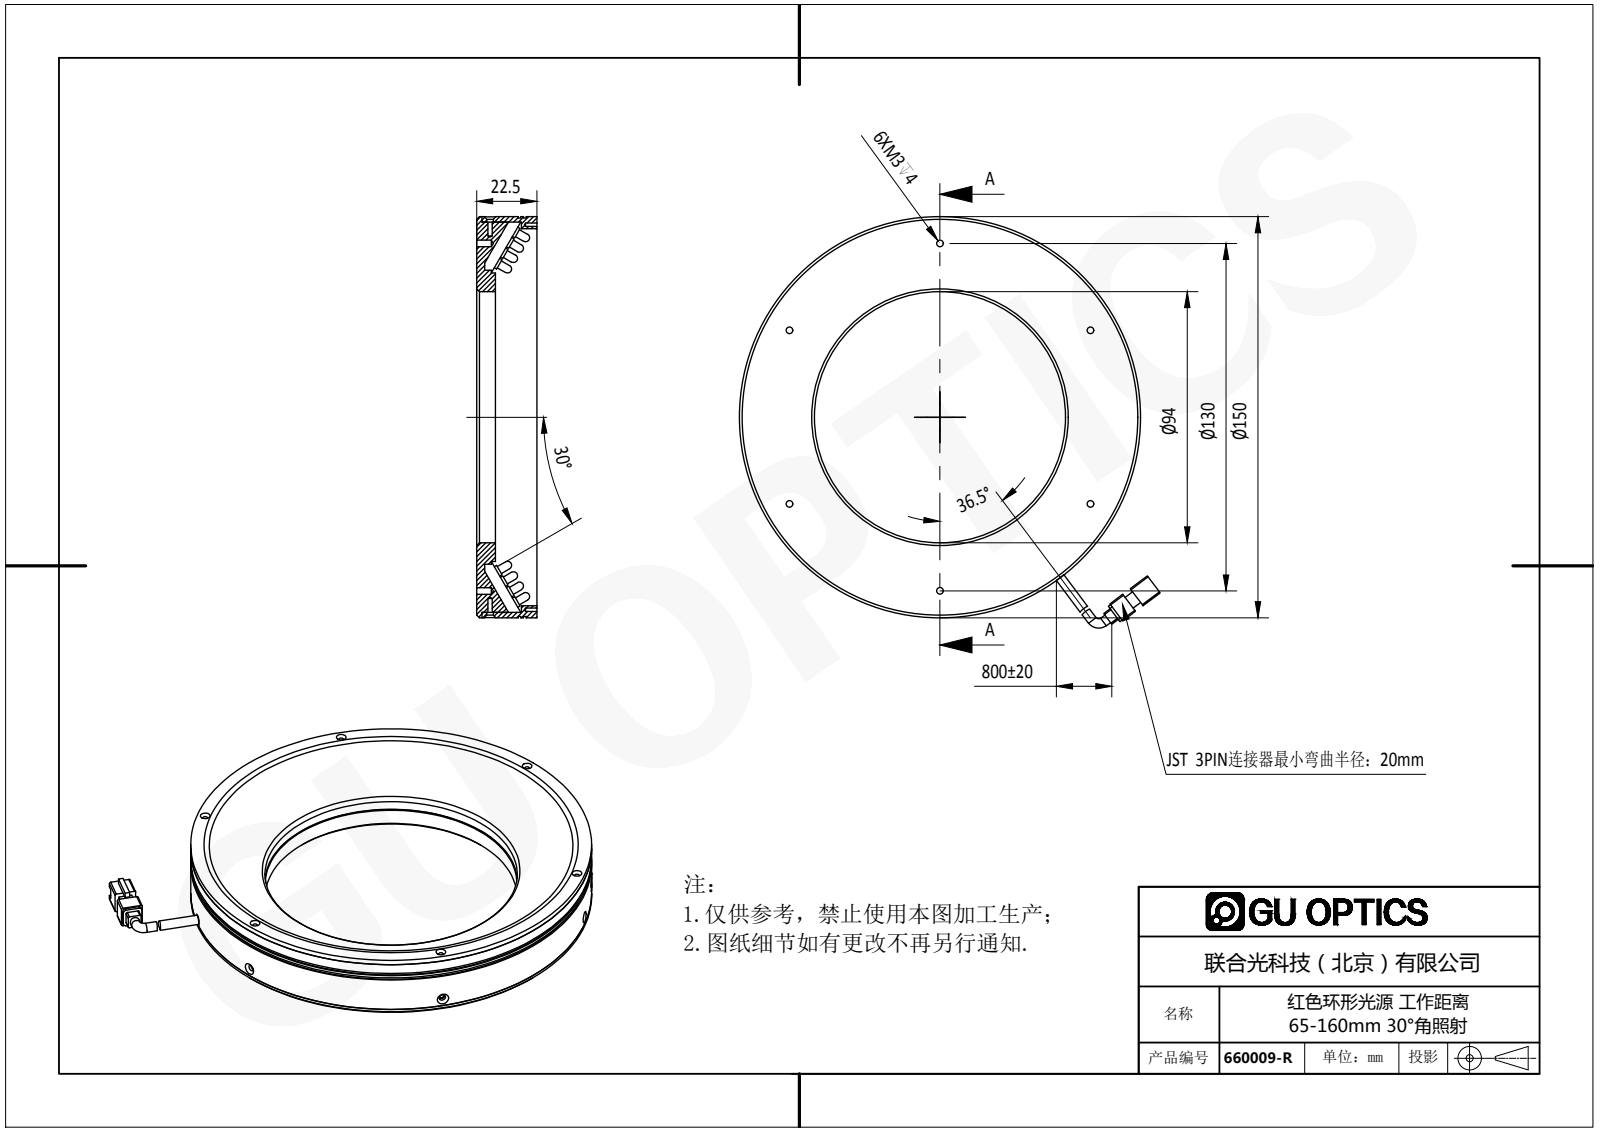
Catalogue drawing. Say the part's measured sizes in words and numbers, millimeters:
The part is named "660009-R". Its 3-D file was written by "SolidWorks 2016 (AUTOMOTIVE_DESIGN)". It is 341 solids with 6006 faces: 4098 planar, 1478 cylindrical and 430 other. Overall it measures 160.52 by 150 by 24.75 millimeters. Its volume is 136 685 cubic millimeters and its surface area 129 773 square millimeters. Round holes: 6 of diameter 1.25, 6 of diameter 1.7, 6 of diameter 2.5, 5 of diameter 1.6, 5 of diameter 2.4, 4 of diameter 3.5, 1 of diameter 94, 1 of diameter 94.4, 1 of diameter 141. Round bosses or shafts: 335 of diameter 3.8, 335 of diameter 3, 2 of diameter 3.5, 1 of diameter 150, 1 of diameter 149, 1 of diameter 146, 1 of diameter 110, 1 of diameter 108. Partial cylindrical surfaces (rounded edges, fillets, slot ends): 8 of radius 0.5, 4 of radius 1, 1 of radius 1.65, 1 of radius 10. The main face-to-face distances are 22.5, 2, 15.5, 7, 1, 17.5, 5, 24.5, 20.5, 3. The hole center spacings are 65, 68.77, 118.7, 72, 112.58, 124.71, 137, 7.
